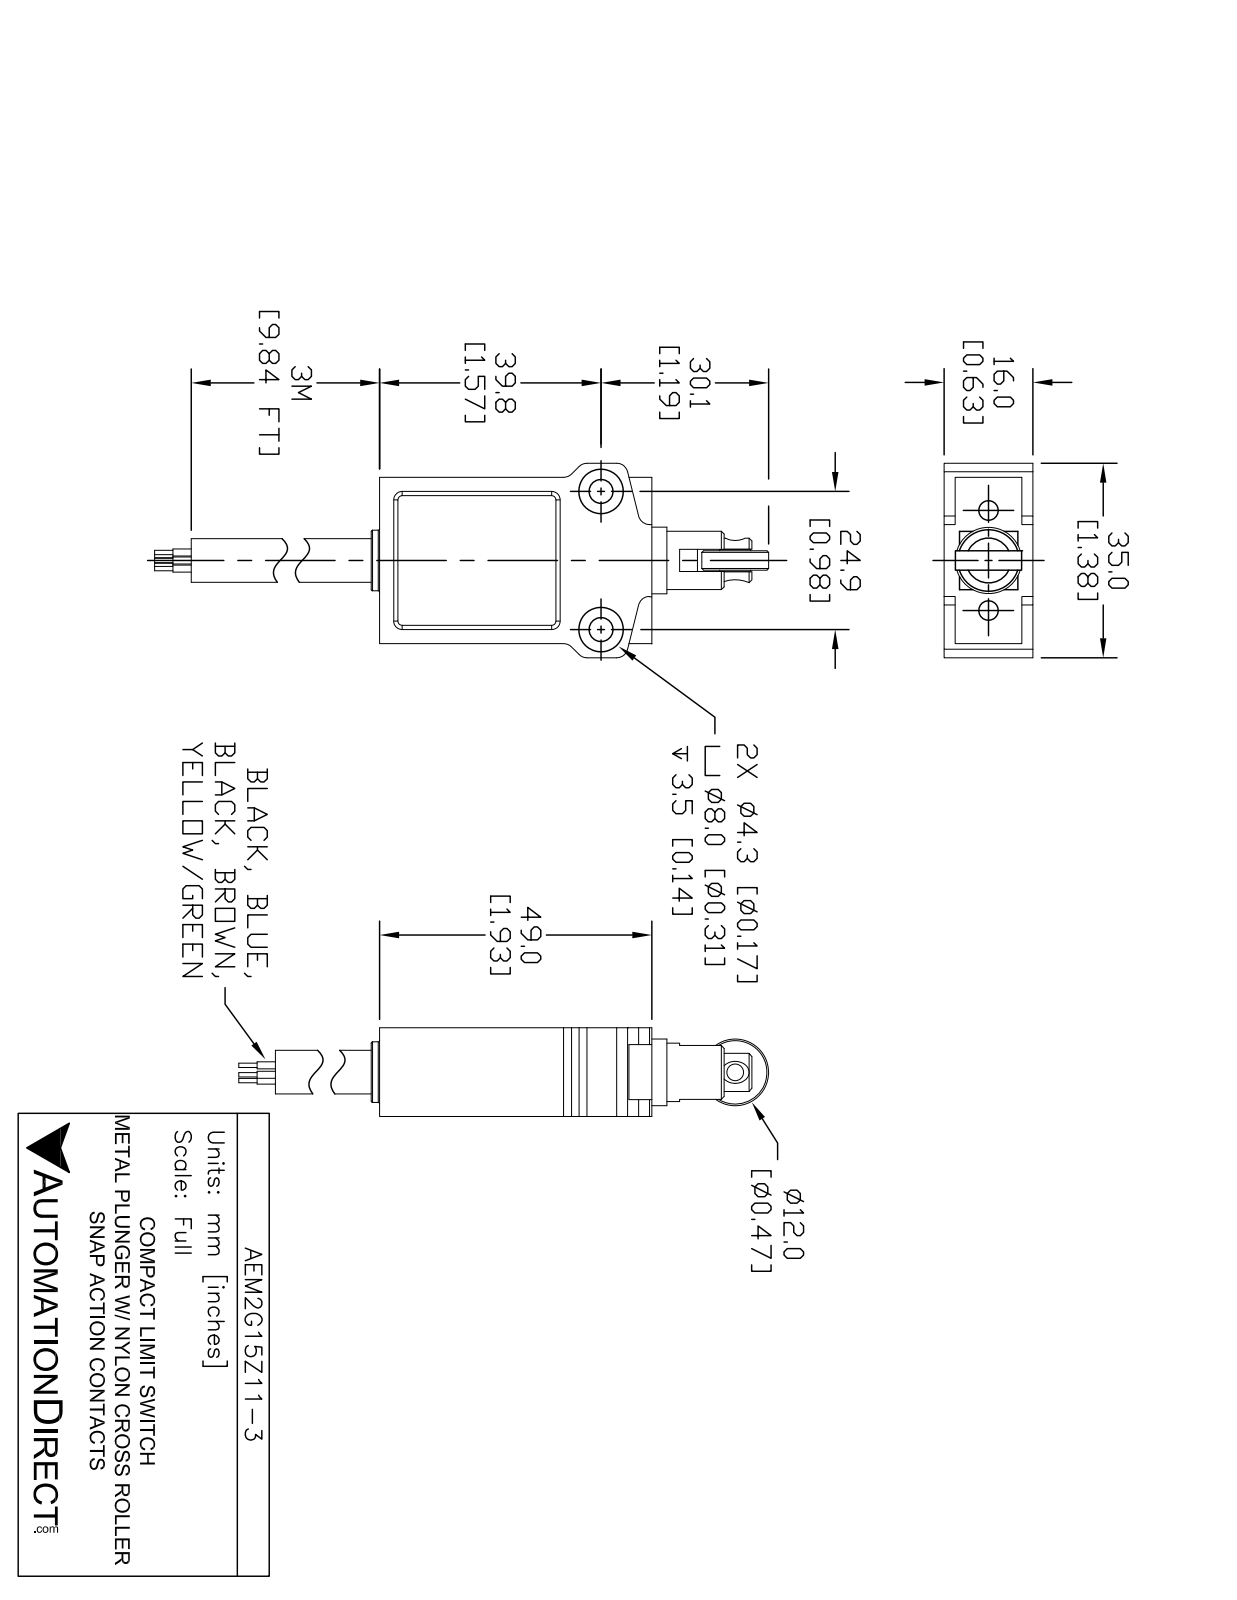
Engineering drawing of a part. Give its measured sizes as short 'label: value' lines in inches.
name: AEM2G15Z11-3_Default
written by: SolidWorks 2021 (CONFIG_CONTROL_DESIGN)
unit: in
bodies: 2 solids, 115 faces (54 planar, 41 cylindrical, 20 other)
size: 3.385 × 1.38 × 0.63
volume: 1.43 in³; area: 11.87 in²
holes: 2× ⌀0.177, 2× ⌀0.344
bosses: 5× ⌀0.05, 5× ⌀0.031, 2× ⌀0.47, 1× ⌀0.43, 1× ⌀0.41, 1× ⌀0.31
rounds: 8× R0.03, 8× R0.08, 1× R0.135
face distances: 0.03, 0.6, 0.57, 0.63, 1.18, 1.93, 0.51, 0.67, 0.505, 0.675
hole spacings: 0.98
